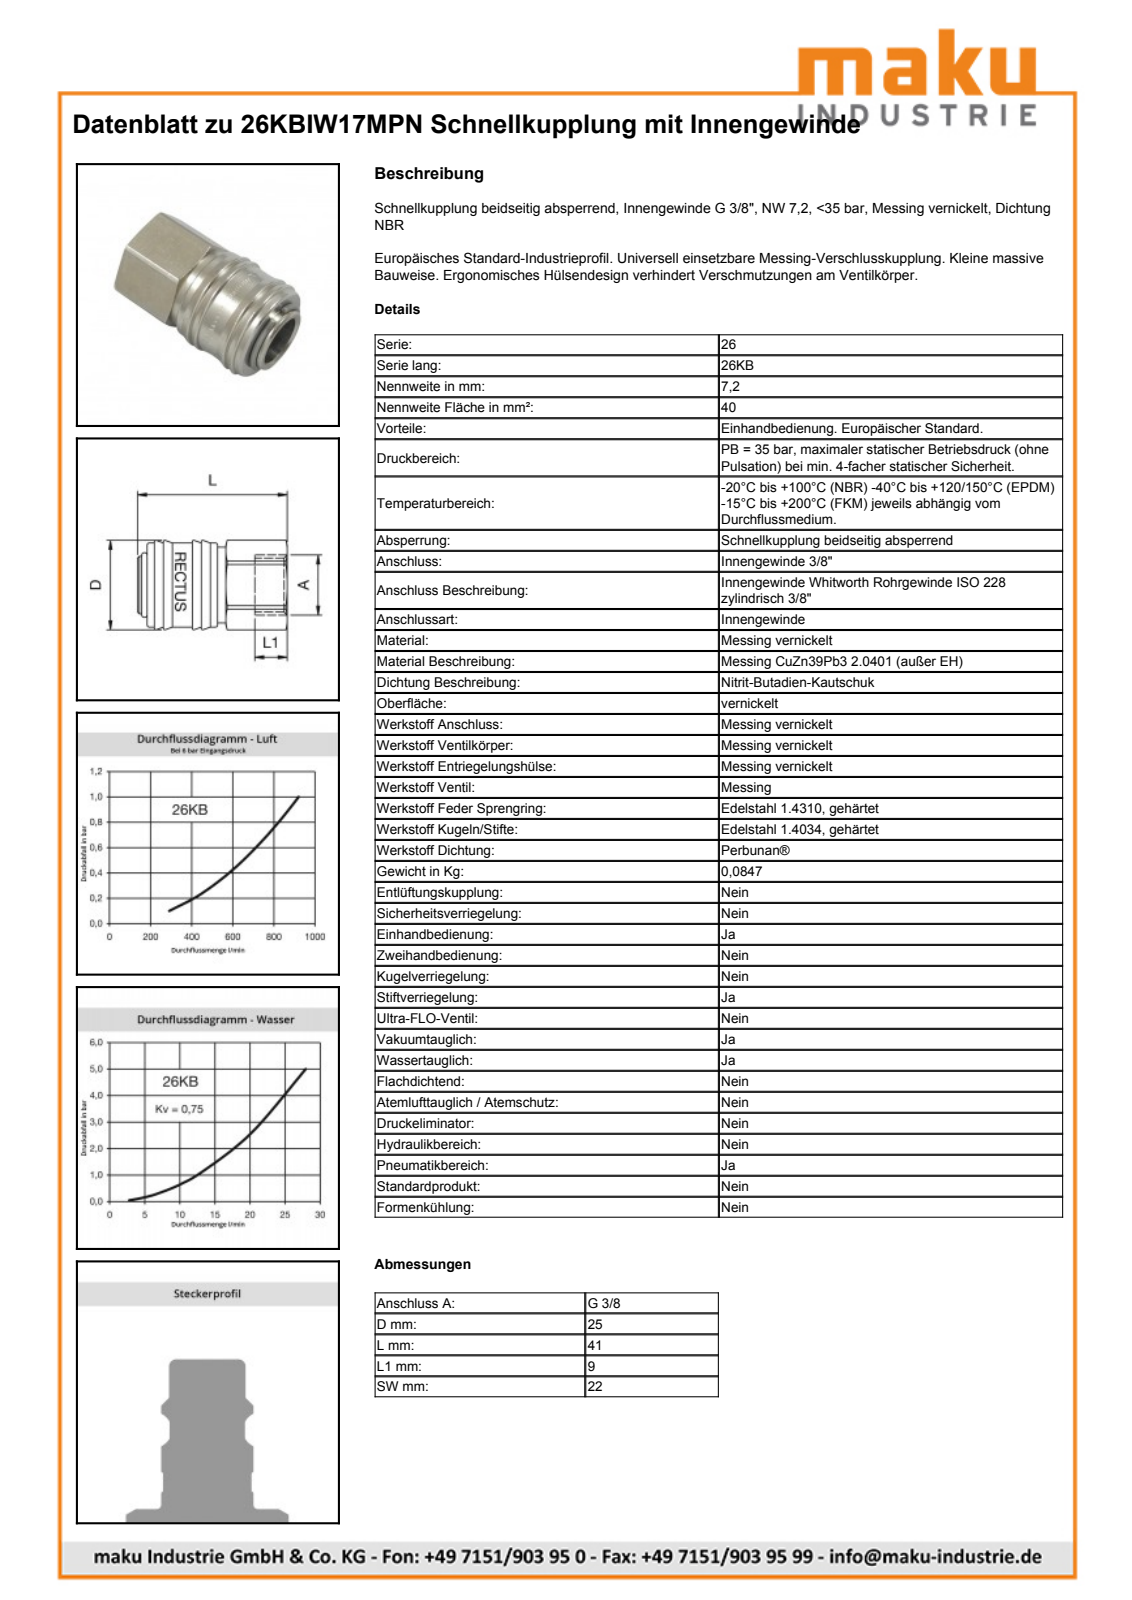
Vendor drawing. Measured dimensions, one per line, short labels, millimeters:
name: D104872
written by: Autodesk Inventor 2011 (AUTOMOTIVE_DESIGN)
unit: mm
bodies: 2 solids, 559 faces (231 planar, 73 cylindrical, 255 other)
size: 41.1 × 24.8 × 24.8
volume: 13 208 mm³; area: 8 925 mm²
holes: 1× ⌀14.45, 1× ⌀14.55, 1× ⌀14.95, 1× ⌀15.45, 1× ⌀16.1, 1× ⌀17, 1× ⌀21.1
bosses: 1× ⌀23.3, 1× ⌀21, 1× ⌀18, 1× ⌀16.65, 1× ⌀15.95, 1× ⌀13.66
rounds: 1× R11.55, 1× R12.4
face distances: 22, 9, 29.45, 2.65, 32.1, 41.1, 38.45, 21, 11.1, 18.35
